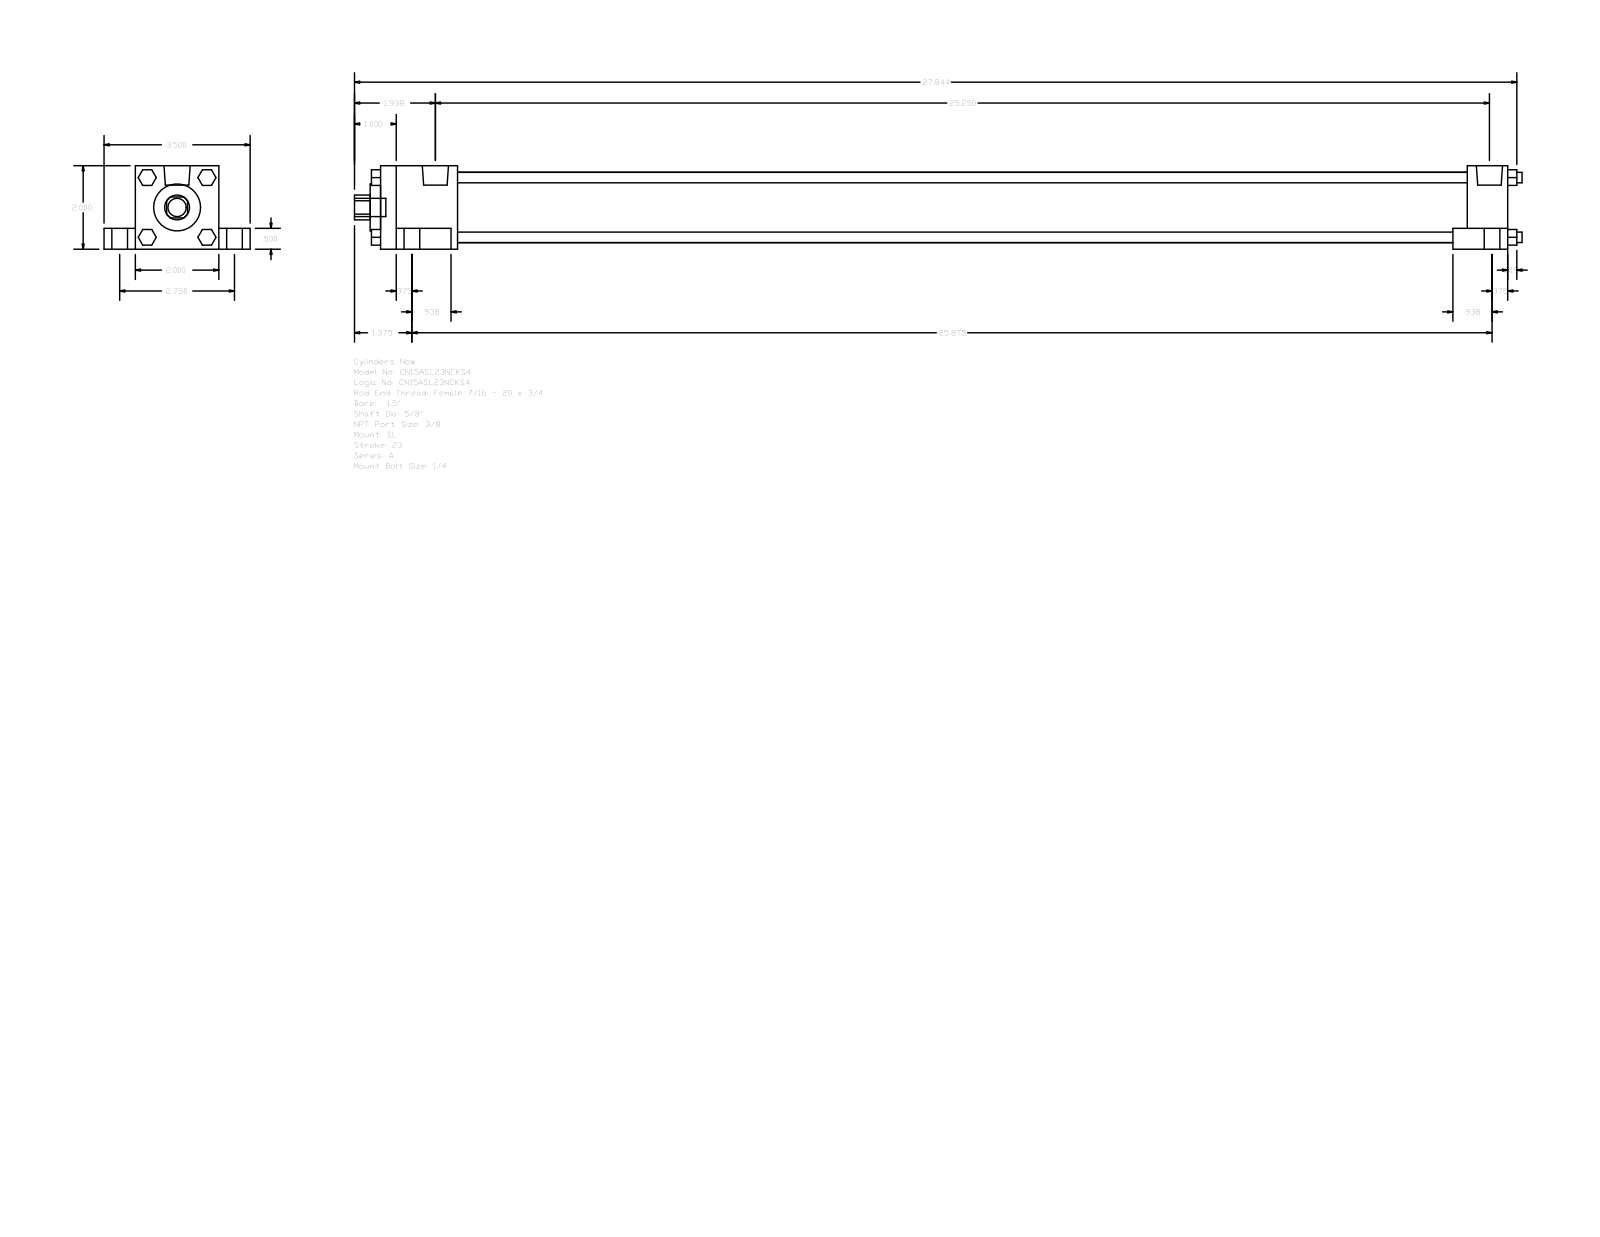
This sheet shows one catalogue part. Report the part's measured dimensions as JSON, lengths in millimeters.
{"part_name": "A_SL__0150_0.625", "step_written_by": "GSSL Pune (CONFIG_CONTROL_DESIGN)", "units": "millimeters", "bodies": {"solids": 0, "faces": 148, "planar": 112, "cylindrical": 36, "other": 0}, "overall_size": [710.41, 88.9, 50.8], "round_holes": [[15.88, 1], [28.57, 1], [42.93, 1]], "round_bosses_or_shafts": [[15.88, 4], [9.53, 4], [6.35, 4], [5.56, 4], [15.93, 2], [11.11, 1]], "partial_cylinders_radius": [[7.54, 1]], "face_to_face_distances": [50.8, 19.05, 12.7, 38.1, 69.85, 685.79, 9.52, 661.19, 24.6, 46.83]}
